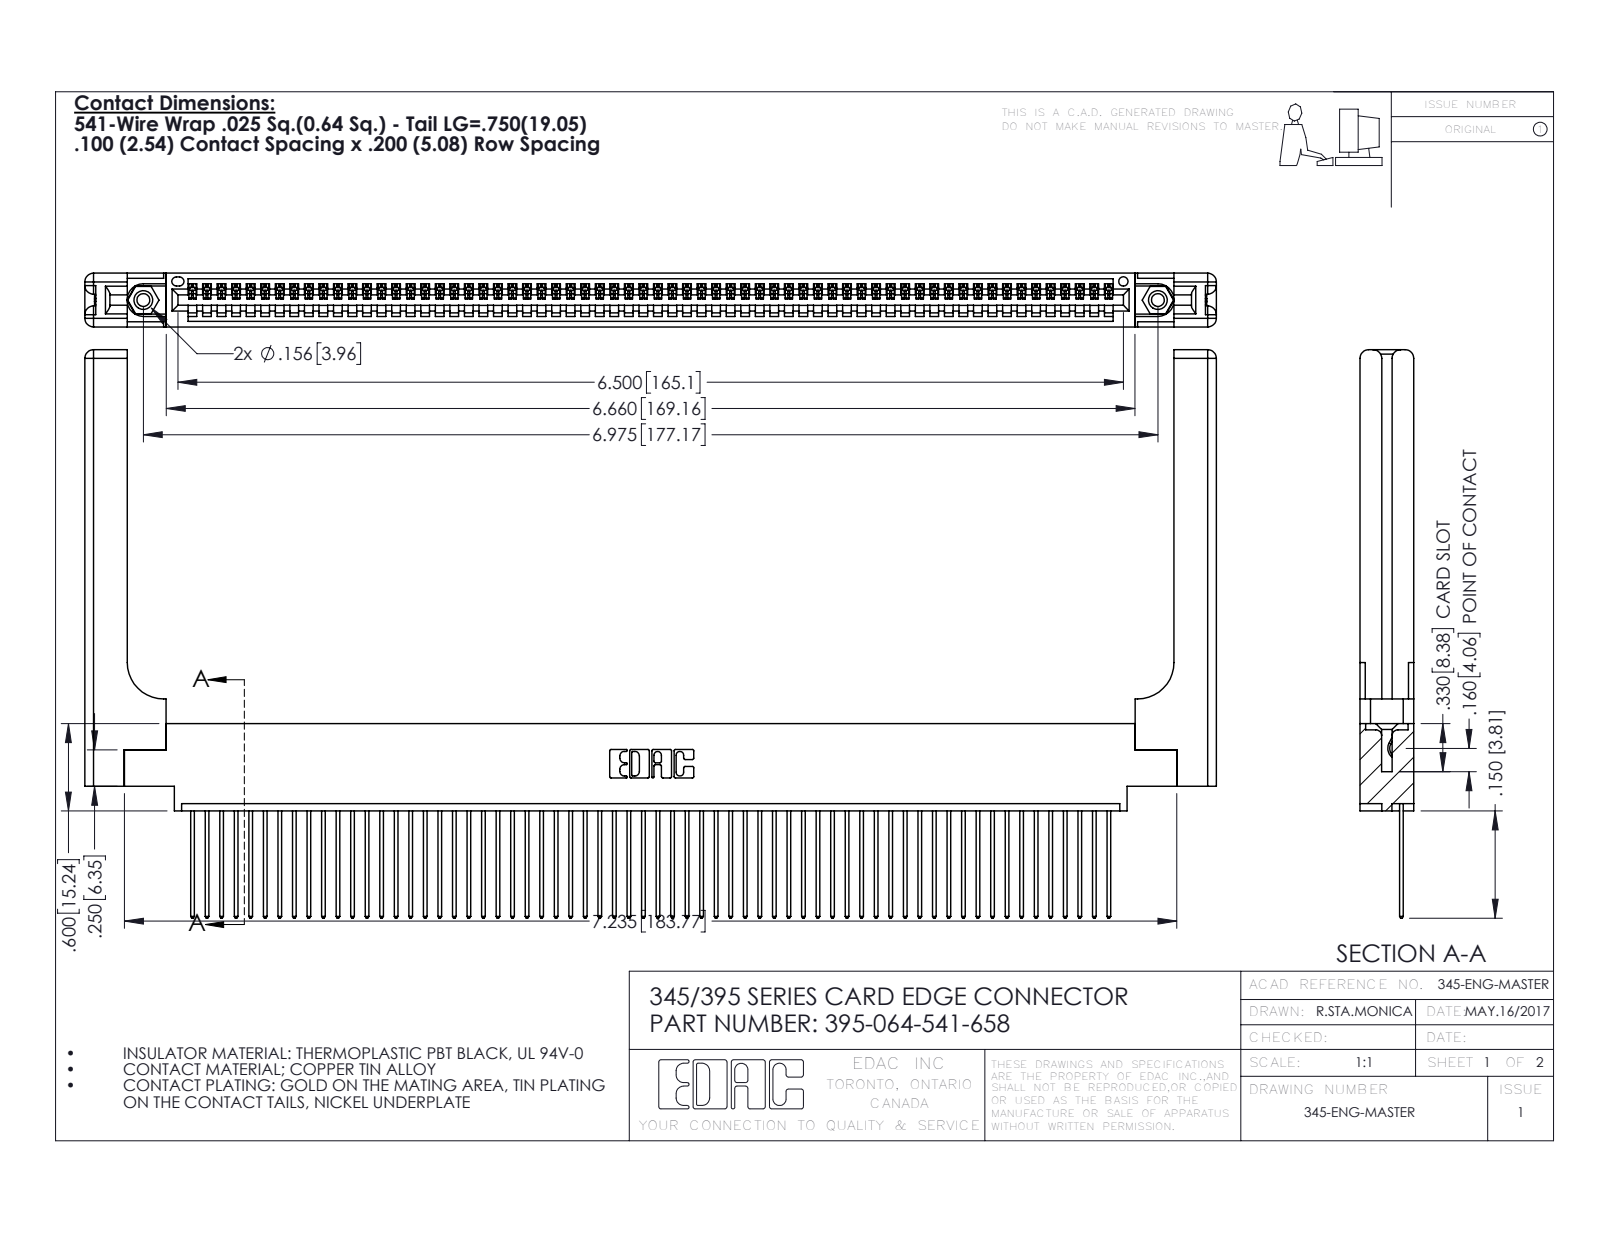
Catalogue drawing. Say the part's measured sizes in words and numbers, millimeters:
The part is named "345 Part_0.170 Offset - 0.156 Dia-TH; 345-250-001_345-250-001-102; 345-292-001_345-293-141; 395-064-541-658 (+1 more)". Its 3-D file was written by "SolidWorks 2016 (CONFIG_CONTROL_DESIGN)". It is 69 solids with 4098 faces: 2792 planar, 1246 cylindrical and 60 other. Overall it measures 197.6 by 99.2 by 9.4 millimeters. Its volume is 27 550 cubic millimeters and its surface area 32 280 square millimeters. Round holes: 2 of diameter 2.3, 2 of diameter 3.2, 2 of diameter 4, 1 of diameter 1.6. Round bosses or shafts: 2 of diameter 3.9. Partial cylindrical surfaces (rounded edges, fillets, slot ends): 128 of radius 0.2, 128 of radius 0.3, 22 of radius 0.3, 16 of radius 1.5, 6 of radius 0.2, 6 of radius 0.8, 3 of radius 0.7, 2 of radius 0.8. The main face-to-face distances are 1.8, 7.6, 9.4, 2.5, 6.9, 0.6, 5.1, 5.7, 3.8, 3.8. The hole center spacings are 6.9, 171.2, 177.2.
